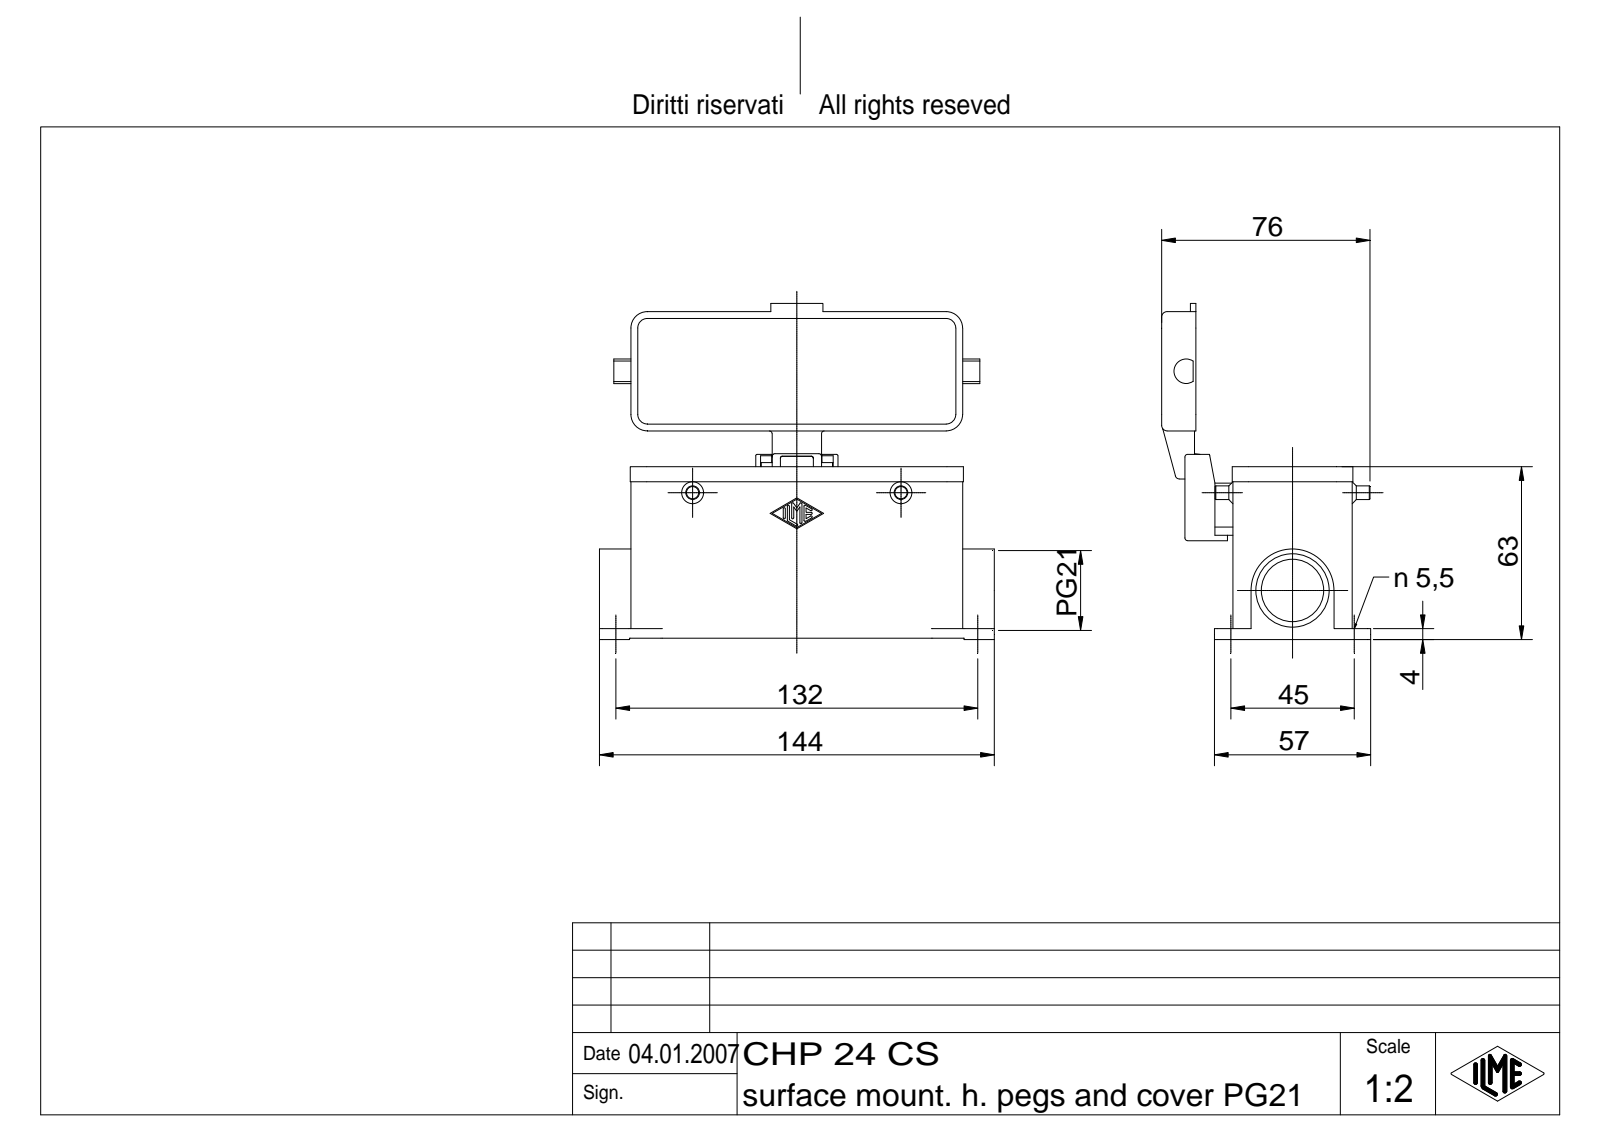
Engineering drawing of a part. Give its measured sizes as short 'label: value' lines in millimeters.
name: CHP 24 CS
written by: Autodesk Inventor 7 (AUTOMOTIVE_DESIGN)
unit: mm
bodies: 2 solids, 475 faces (177 planar, 177 cylindrical, 121 other)
size: 144 × 122.5 × 76.25
volume: 136 554 mm³; area: 78 743 mm²
holes: 4× ⌀5.5, 1× ⌀4, 1× ⌀5, 1× ⌀22.78, 1× ⌀26.78
bosses: 2× ⌀5, 2× ⌀3, 1× ⌀7, 1× ⌀4
rounds: 26× R1, 14× R0.38, 12× R6, 9× R0.5, 8× R0.7, 8× R2, 4× R3, 4× R3.5
face distances: 3, 40.5, 3.5, 43.5, 37.5, 63, 69.5, 66.5, 22.5, 29
hole spacings: 45, 132, 139.46
